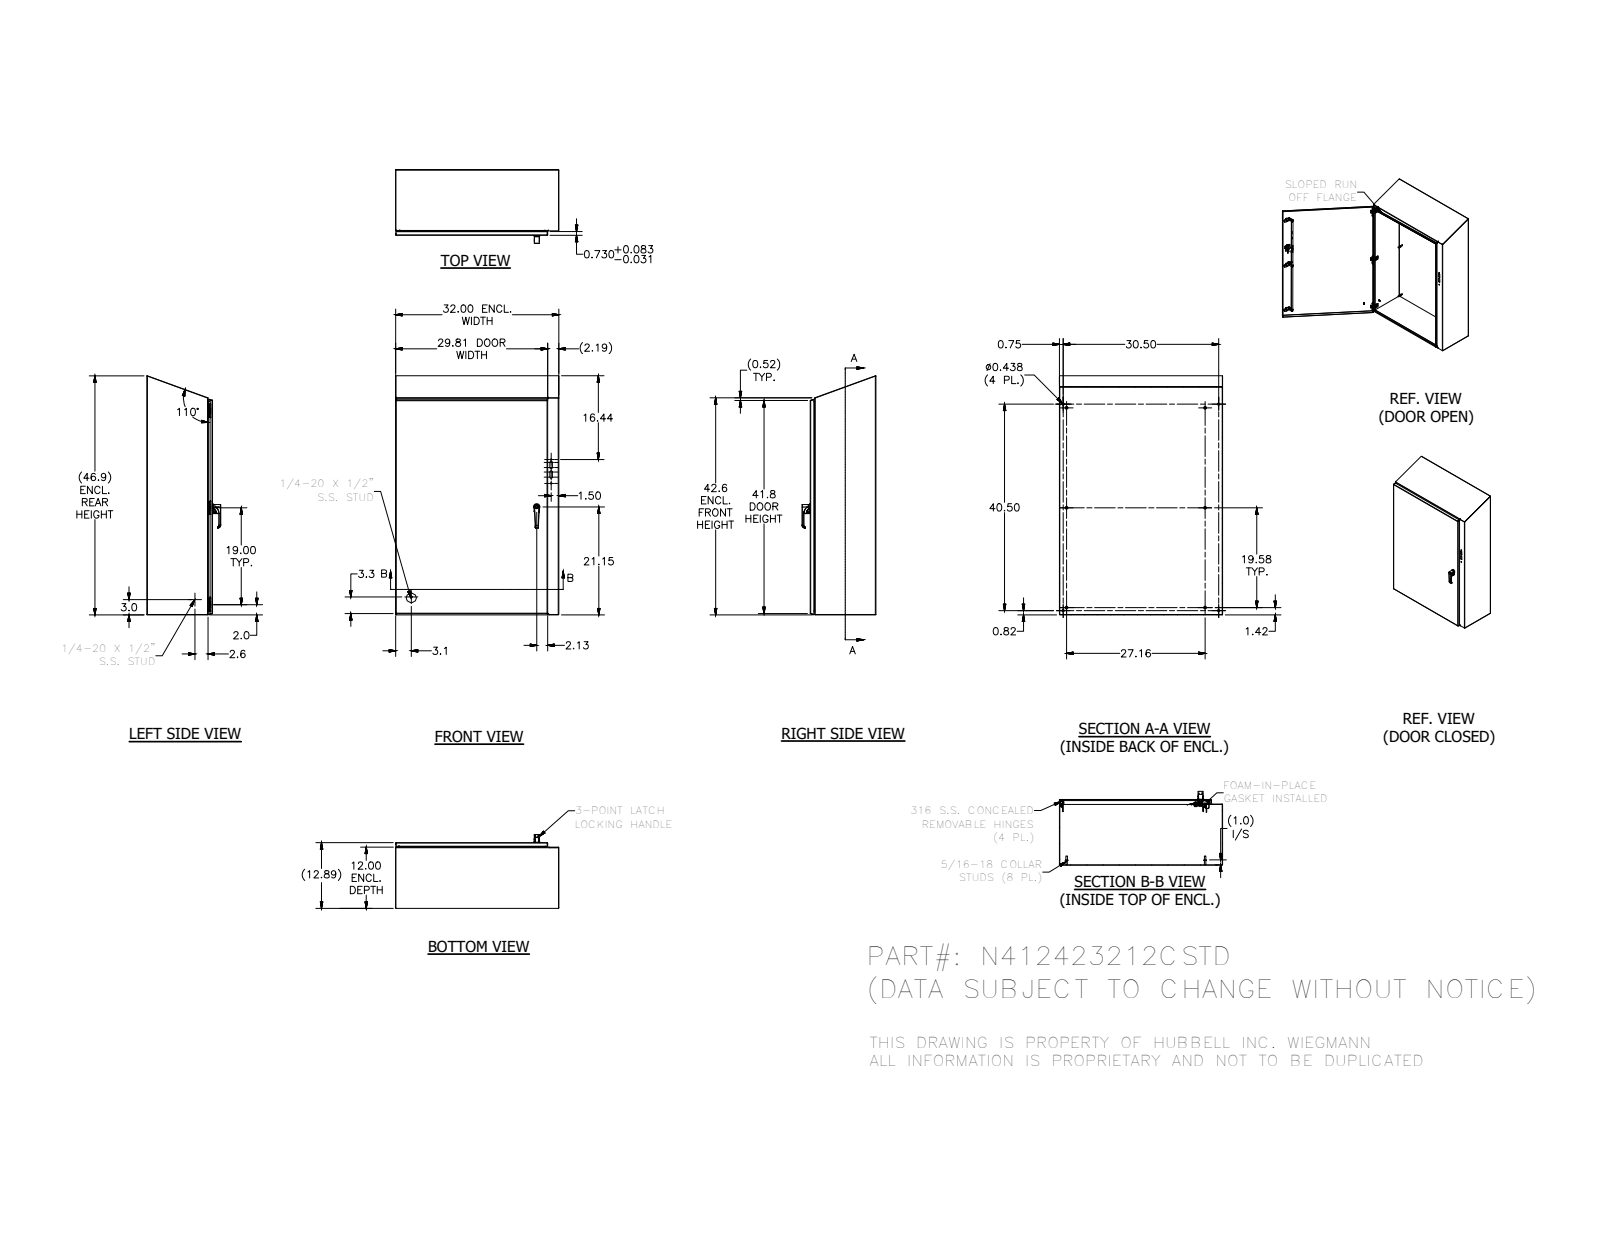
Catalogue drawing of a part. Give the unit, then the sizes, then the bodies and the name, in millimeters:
Units: millimetres
Overall size (bounding box): 1191.14 × 812.8 × 367.82
Round holes (diameter × count): ⌀2.36 ×6, ⌀3.68 ×6, ⌀3.86 ×6, ⌀3.96 ×6, ⌀4.25 ×6, ⌀4.37 ×6, ⌀4.76 ×6, ⌀8.13 ×4, ⌀11.11 ×4, ⌀4.98 ×3, ⌀5.36 ×3, ⌀5.59 ×3
Round bosses / shafts (diameter × count): ⌀6.35 ×16, ⌀7.62 ×12, ⌀14.3 ×6, ⌀11.11 ×6, ⌀9.14 ×6, ⌀8.13 ×6, ⌀6.99 ×6, ⌀6.5 ×6
Partial cylindrical surfaces — rounded edges, fillets, slot ends (radius × count): R0.5 ×38, R1.27 ×38, R3.17 ×37, R0.79 ×32, R0.3 ×30, R0.4 ×26, R0.64 ×24, R2.67 ×18
Main face-to-face distances: 1.88, 325.44, 323.56, 327.32, 810.92, 809.04, 812.8, 302.92, 22.52, 20.64
Hole centre spacings: 482.6, 12.7, 965.2, 906.46, 449.26, 457.2, 482.77, 906.47
Volume: 6 223 000 mm³ · Surface area: 6 581 000 mm²
Bodies: 82 solids, 2693 faces (1049 planar, 965 cylindrical, 679 other)
Part name (STEP PRODUCT): N412423212CSTDBLR; 388150; N4123212CSTDTOP; 38846 (+8 more)
STEP written by: Autodesk Inventor 2014 (AUTOMOTIVE_DESIGN)
